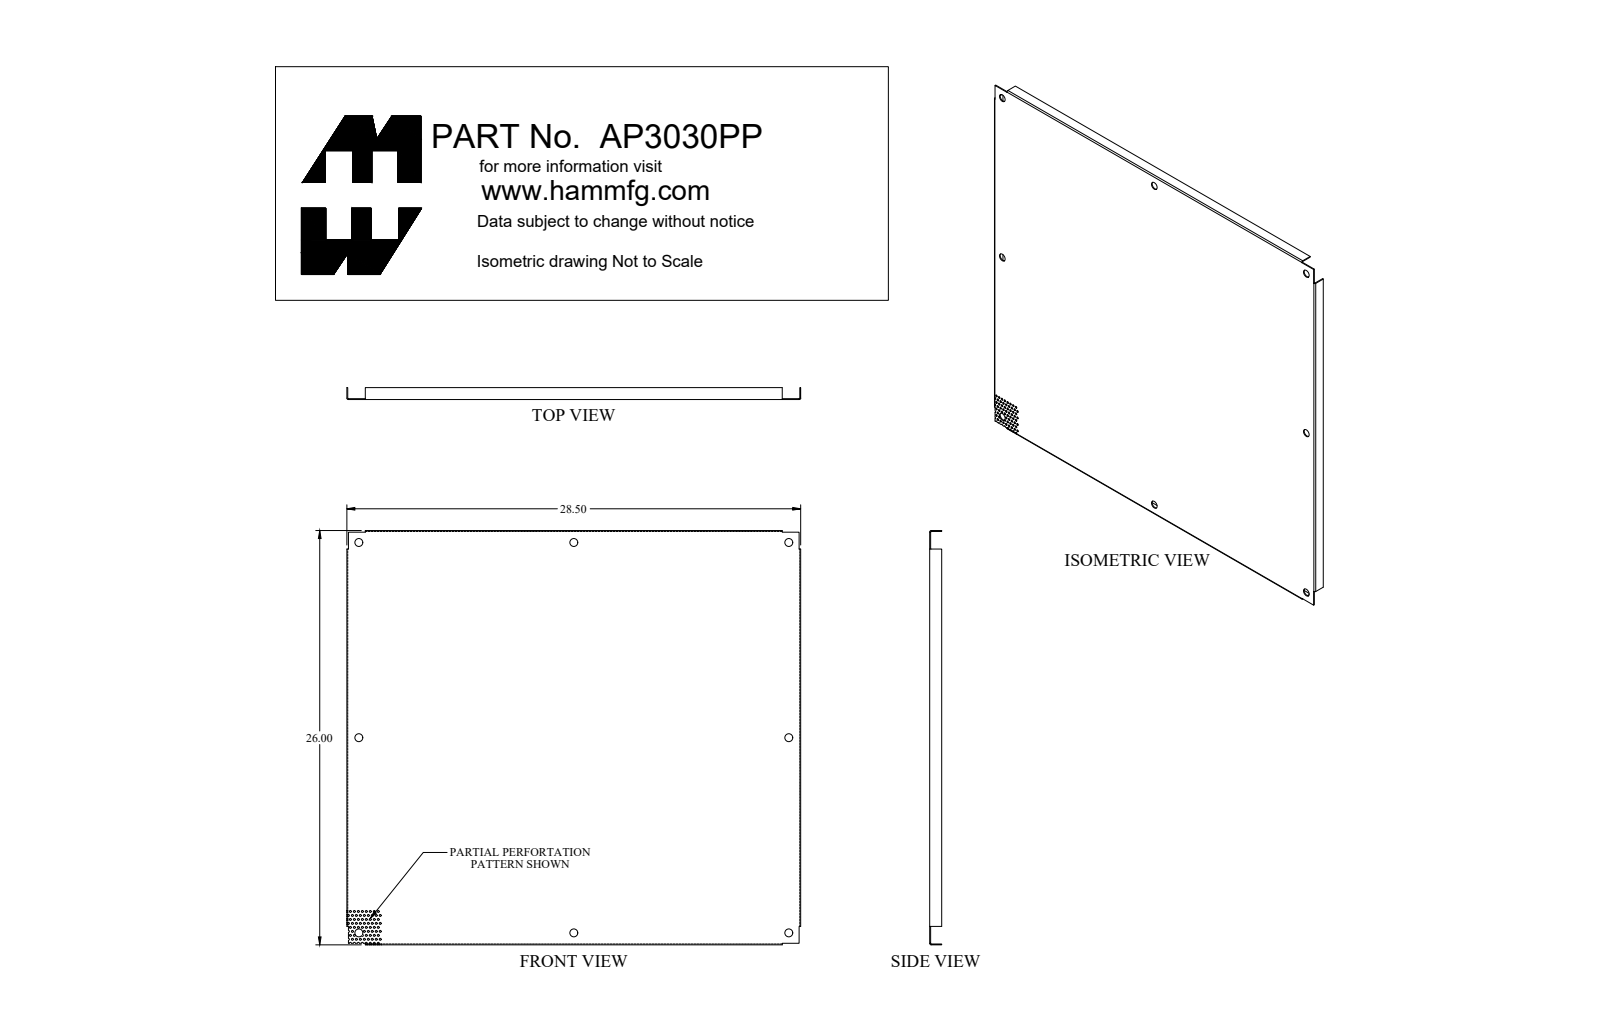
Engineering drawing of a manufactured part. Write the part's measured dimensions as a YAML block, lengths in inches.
part_name: "AP3030PP_Default"
step_written_by: "SolidWorks 2019 (CONFIG_CONTROL_DESIGN)"
units: inches
bodies: {solids: 1, faces: 268, planar: 43, cylindrical: 217, other: 8}
overall_size: [28.5, 26, 0.75]
volume: 45.83
surface_area: 1617
round_holes:
  - {diameter: 0.125, count: 74}
  - {diameter: 0.5, count: 8}
  - {diameter: 0.125, count: 2}
partial_cylinders:
  - {radius: 0.063, count: 15}
  - {radius: 0.062, count: 6}
  - {radius: 0.029, count: 4}
  - {radius: 0.086, count: 4}
face_to_face_distances: [0.057, 25.943, 28.443, 26, 25.886, 28.386, 28.5, 0.75, 0.693, 0.102]
hole_center_spacings: [0.28, 0.5, 0.25, 0.559, 0.451, 0.76, 0.673, 0.75]
